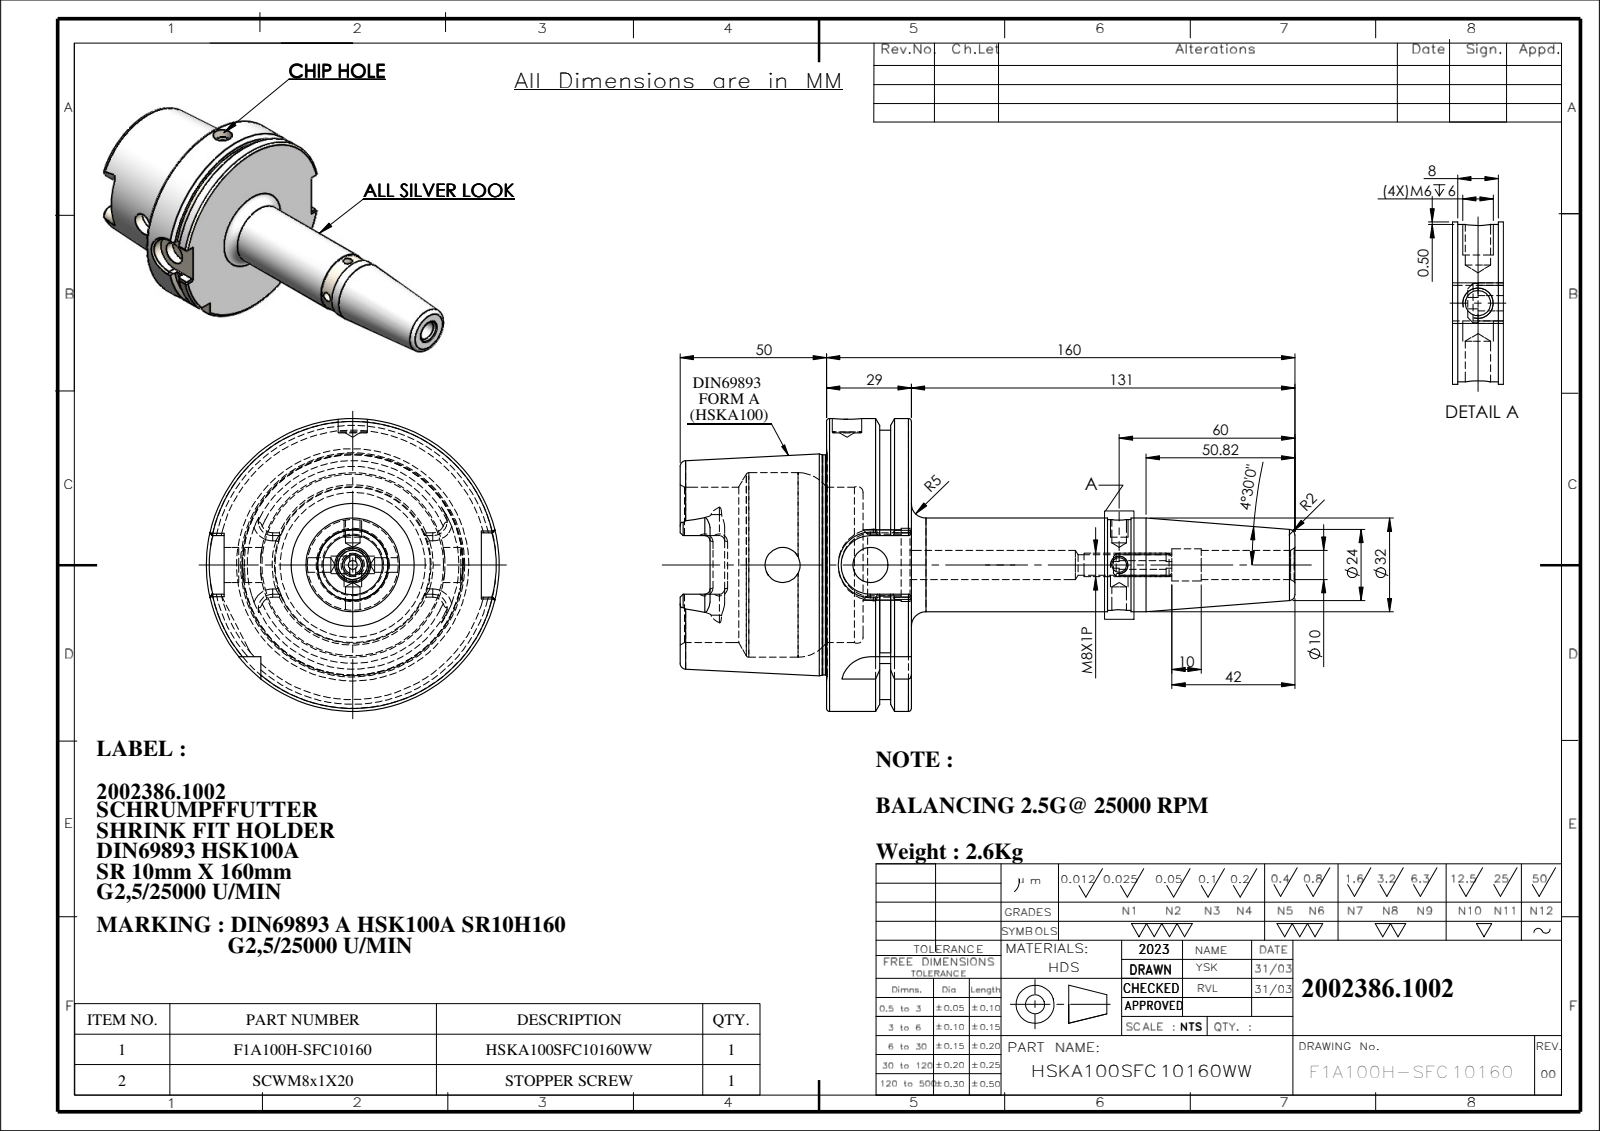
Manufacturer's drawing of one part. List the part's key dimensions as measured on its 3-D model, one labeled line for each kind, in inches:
Part name (STEP PRODUCT): 91100A-SR10160; HSKA100SFC10160WW; SCWM8X1
STEP written by: SolidWorks 2018 (CONFIG_CONTROL_DESIGN)
Units: inches
Bodies: 2 solids, 227 faces (71 planar, 70 cylindrical, 86 other)
Overall size (bounding box): 8.266 × 3.937 × 3.937
Volume: 20.79 in³ · Surface area: 103.8 in²
Round holes (diameter × count): ⌀0.197 ×2, ⌀0.394 ×2, ⌀0.472 ×2, ⌀0.118 ×1, ⌀0.276 ×1, ⌀0.393 ×1, ⌀0.432 ×1, ⌀0.827 ×1, ⌀0.984 ×1, ⌀2.087 ×1, ⌀2.48 ×1
Round bosses / shafts (diameter × count): ⌀3.937 ×1, ⌀3.622 ×1, ⌀2.959 ×1, ⌀1.26 ×1, ⌀1.22 ×1, ⌀0.315 ×1
Partial cylindrical surfaces — rounded edges, fillets, slot ends (radius × count): R0.071 ×6, R0.192 ×4, R0.394 ×2, R0.433 ×1
Main face-to-face distances: 1.14, 0.492, 0.648, 1.969, 2.461, 3.108, 0.63, 3.091, 1.122, 0.018
Hole centre spacings: 1.181, 3.344, 3.659, 4.526
